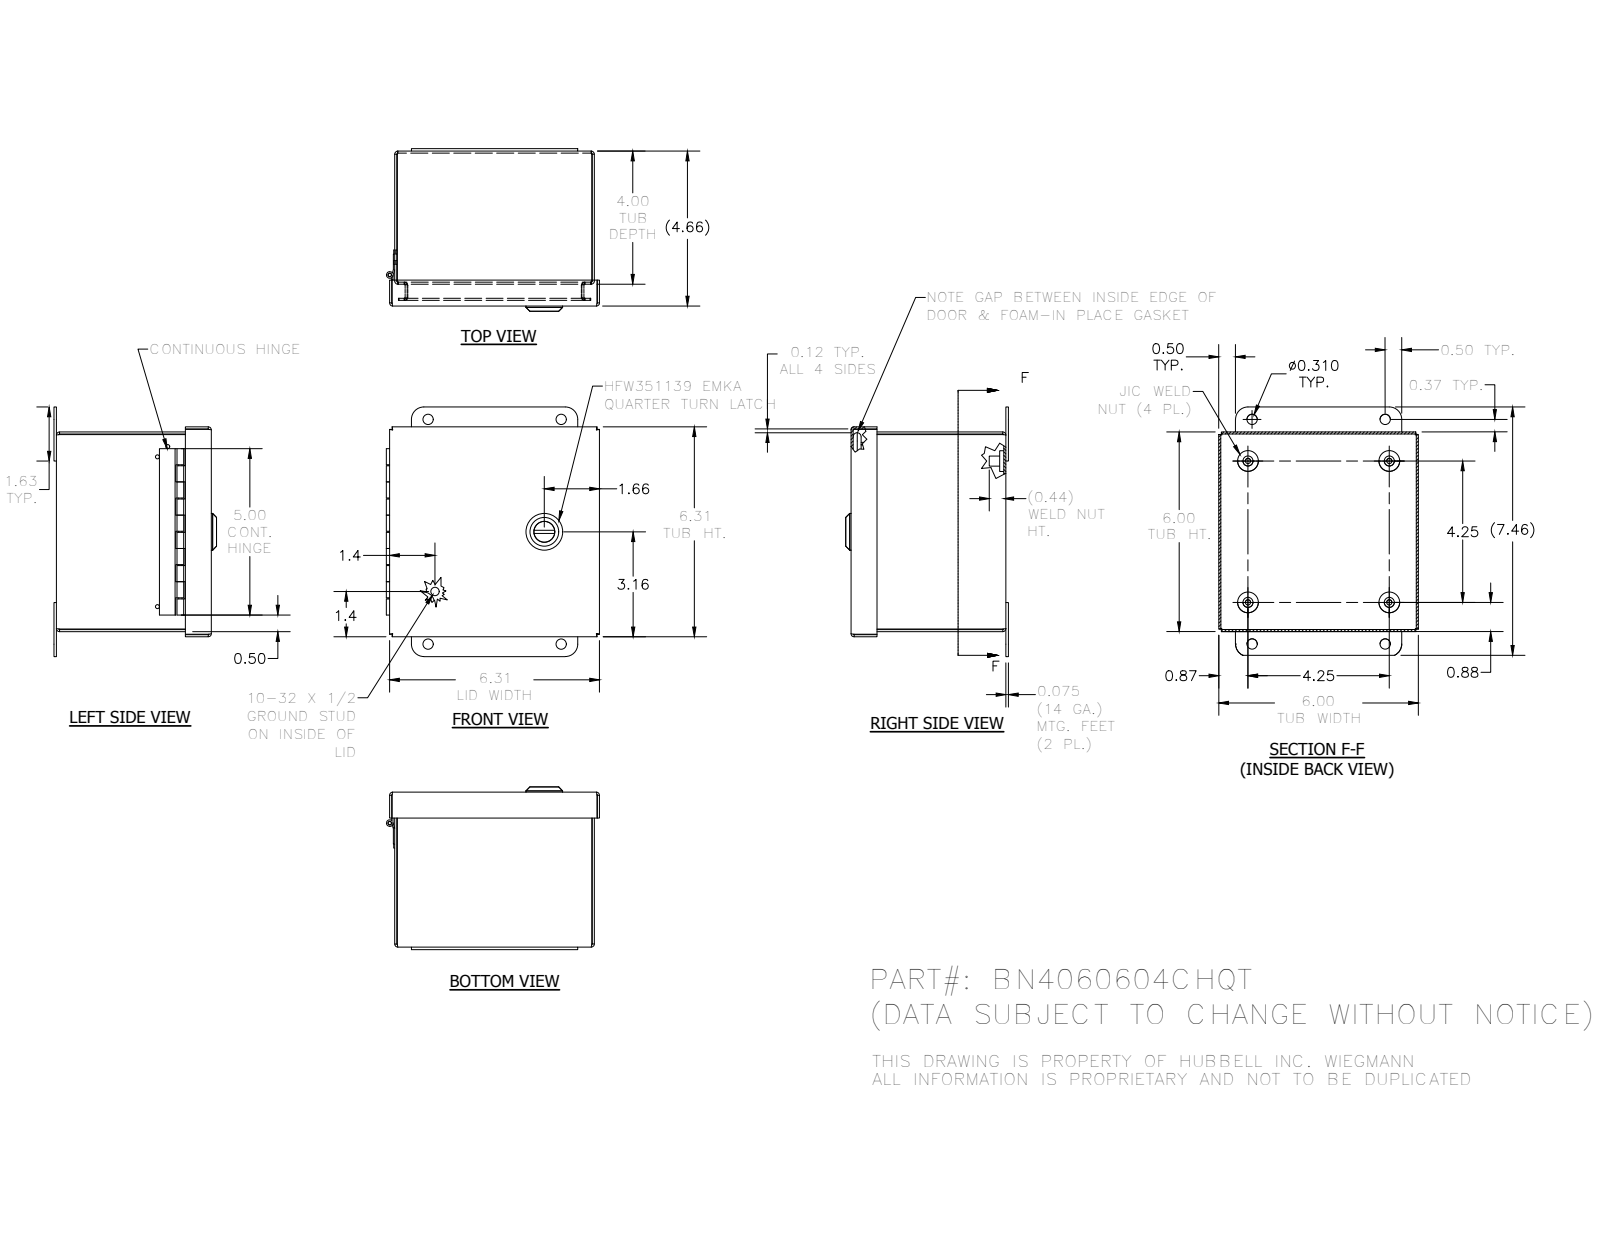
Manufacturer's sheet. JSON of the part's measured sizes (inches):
{"part_name": "BN4060604CHQT_a", "step_written_by": "SolidWorks 2018 (AUTOMOTIVE_DESIGN)", "units": "inches", "bodies": {"solids": 21, "faces": 725, "planar": 360, "cylindrical": 237, "other": 128}, "overall_size": [7.5, 6.406, 4.888], "volume_in3": 17.47, "surface_area_in2": 518.4, "round_holes": [[0.156, 4], [0.31, 4], [0.12, 3], [0.116, 1], [0.197, 1], [0.315, 1], [0.394, 1], [0.402, 1], [0.634, 1], [0.802, 1]], "round_bosses_or_shafts": [[0.625, 4], [0.3, 4], [1.102, 1], [0.866, 1], [0.78, 1], [0.622, 1], [0.598, 1], [0.531, 1]], "partial_cylinders_radius": [[0.012, 30], [0.031, 20], [0.093, 20], [0.125, 16], [0.02, 12], [0.157, 4], [0.375, 4], [0.016, 2]], "face_to_face_distances": [0.062, 0.062, 5.938, 6, 4.594, 4.656, 4.532, 4.594, 6.093, 5.876], "hole_center_spacings": [4.31, 1.256, 4.25, 5.502, 4, 4.198, 6.01, 6.75]}
